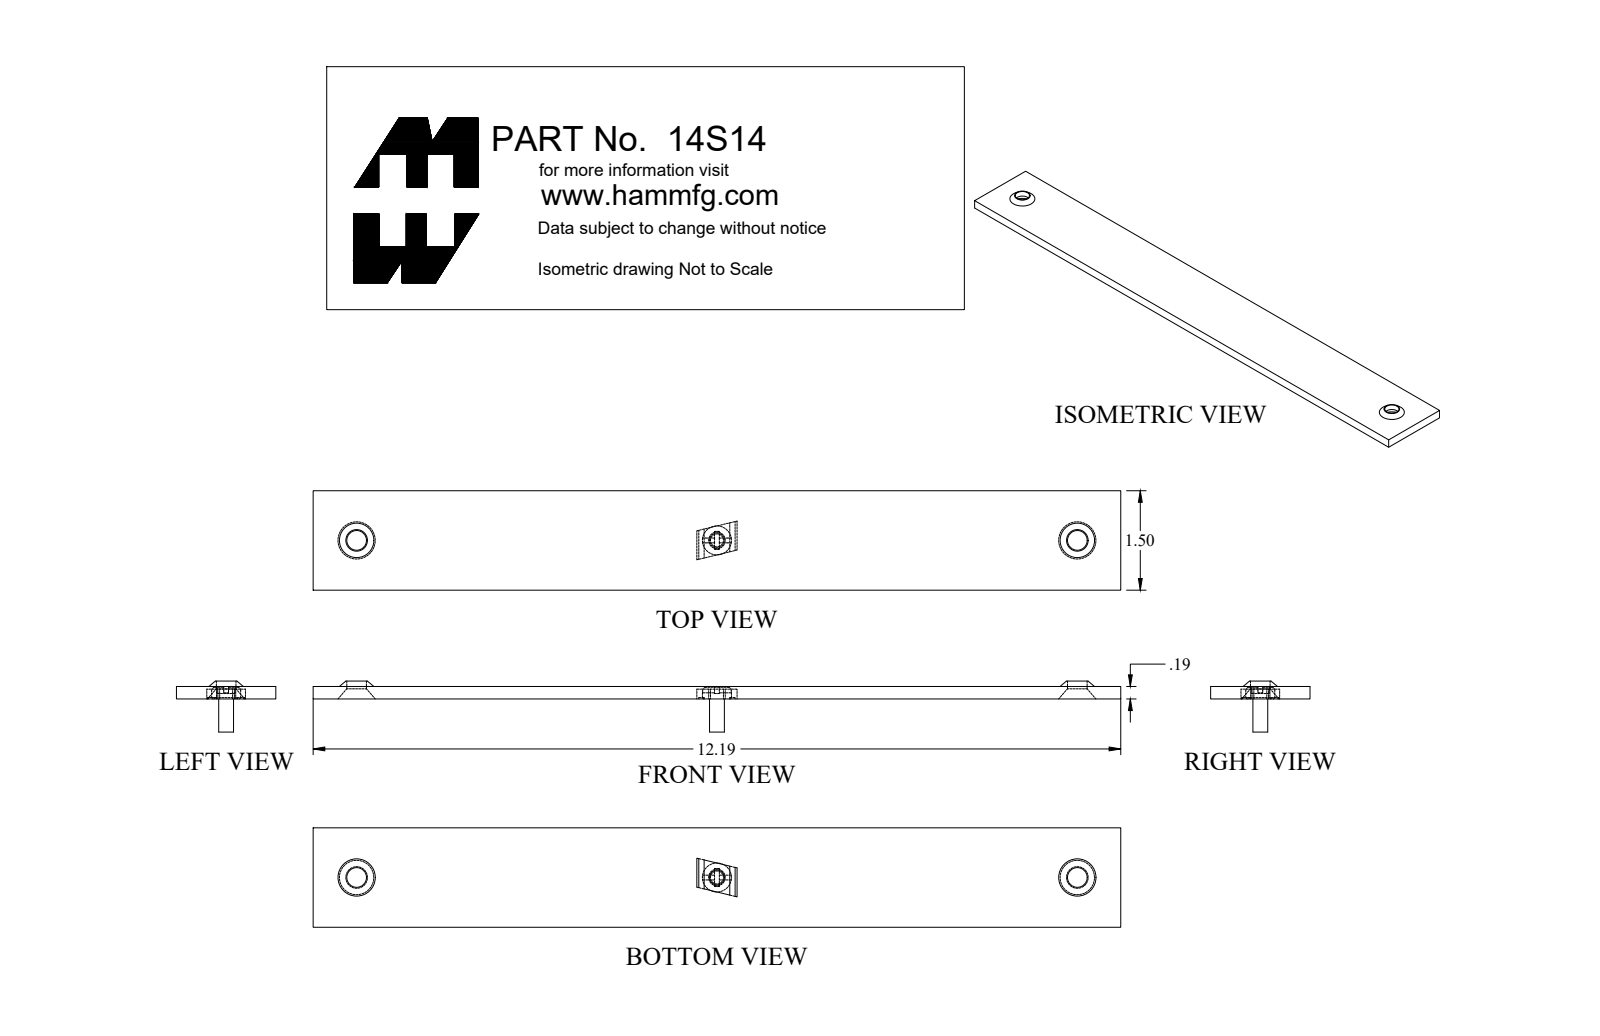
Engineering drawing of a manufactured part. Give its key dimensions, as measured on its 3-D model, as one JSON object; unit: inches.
{"part_name": "14S14", "step_written_by": "SolidWorks 2018 (AUTOMOTIVE_DESIGN)", "units": "inches", "bodies": {"solids": 1, "faces": 14, "planar": 8, "cylindrical": 2, "other": 4}, "overall_size": [12.187, 1.5, 0.27], "volume_in3": 3.398, "surface_area_in2": 41.92, "round_holes": [[0.296, 2]], "face_to_face_distances": [0.188, 1.5, 12.187, 0.27, 0.082], "hole_center_spacings": [10.875]}
